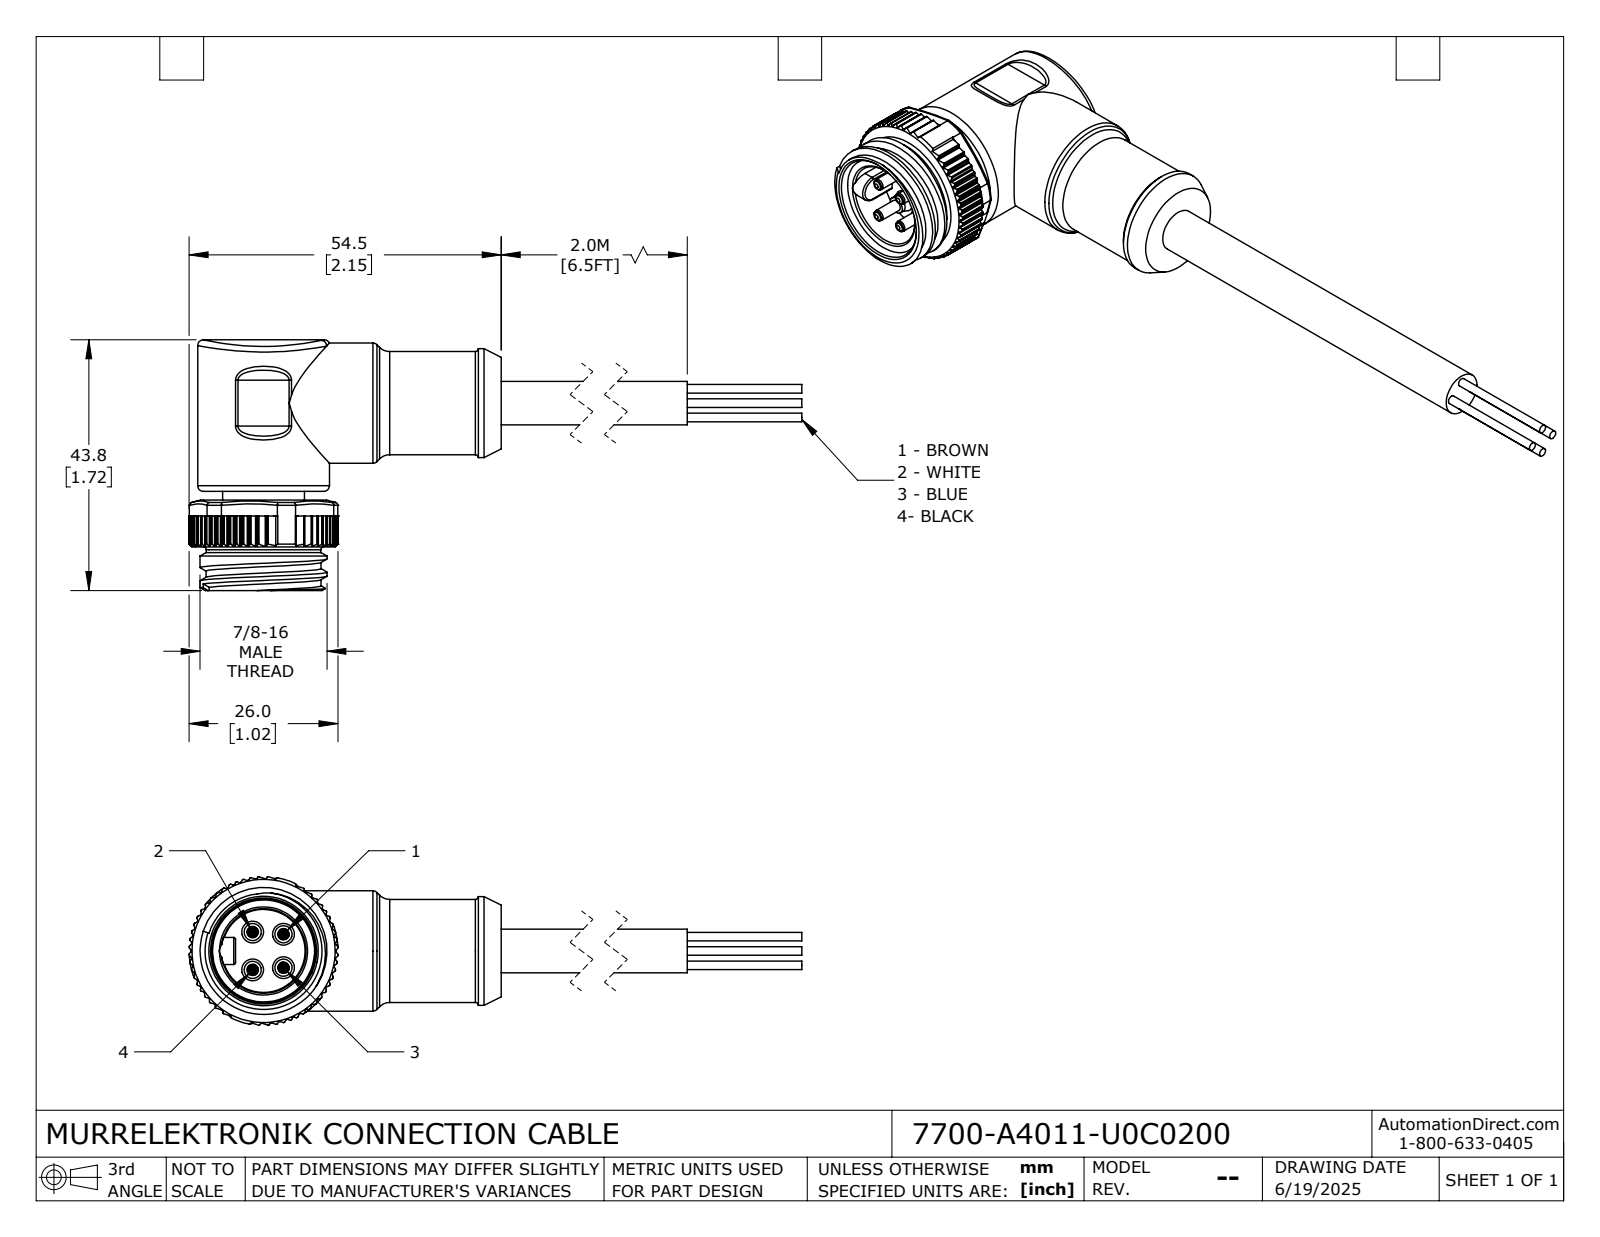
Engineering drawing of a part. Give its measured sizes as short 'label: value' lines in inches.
name: 7700-A4011-U0C0200
written by: SolidWorks 2024 (CONFIG_CONTROL_DESIGN)
unit: in
bodies: 1 solid, 604 faces (238 planar, 282 cylindrical, 84 other)
size: 5.689 × 1.723 × 1.022
volume: 1.726 in³; area: 16.83 in²
holes: 1× ⌀0.614, 1× ⌀0.728
bosses: 4× ⌀0.118, 4× ⌀0.079, 4× ⌀0.059, 1× ⌀0.906, 1× ⌀0.873, 1× ⌀0.827, 1× ⌀0.789, 1× ⌀0.787
rounds: 126× R0.008, 18× R0.012, 4× R0.004, 4× R0.028, 4× R0.039, 4× R0.098, 1× R0.093, 1× R0.512
face distances: 0.059, 0.323, 0.382, 0.035, 0.287, 0.346, 0.622, 0.827, 0.563, 0.24
